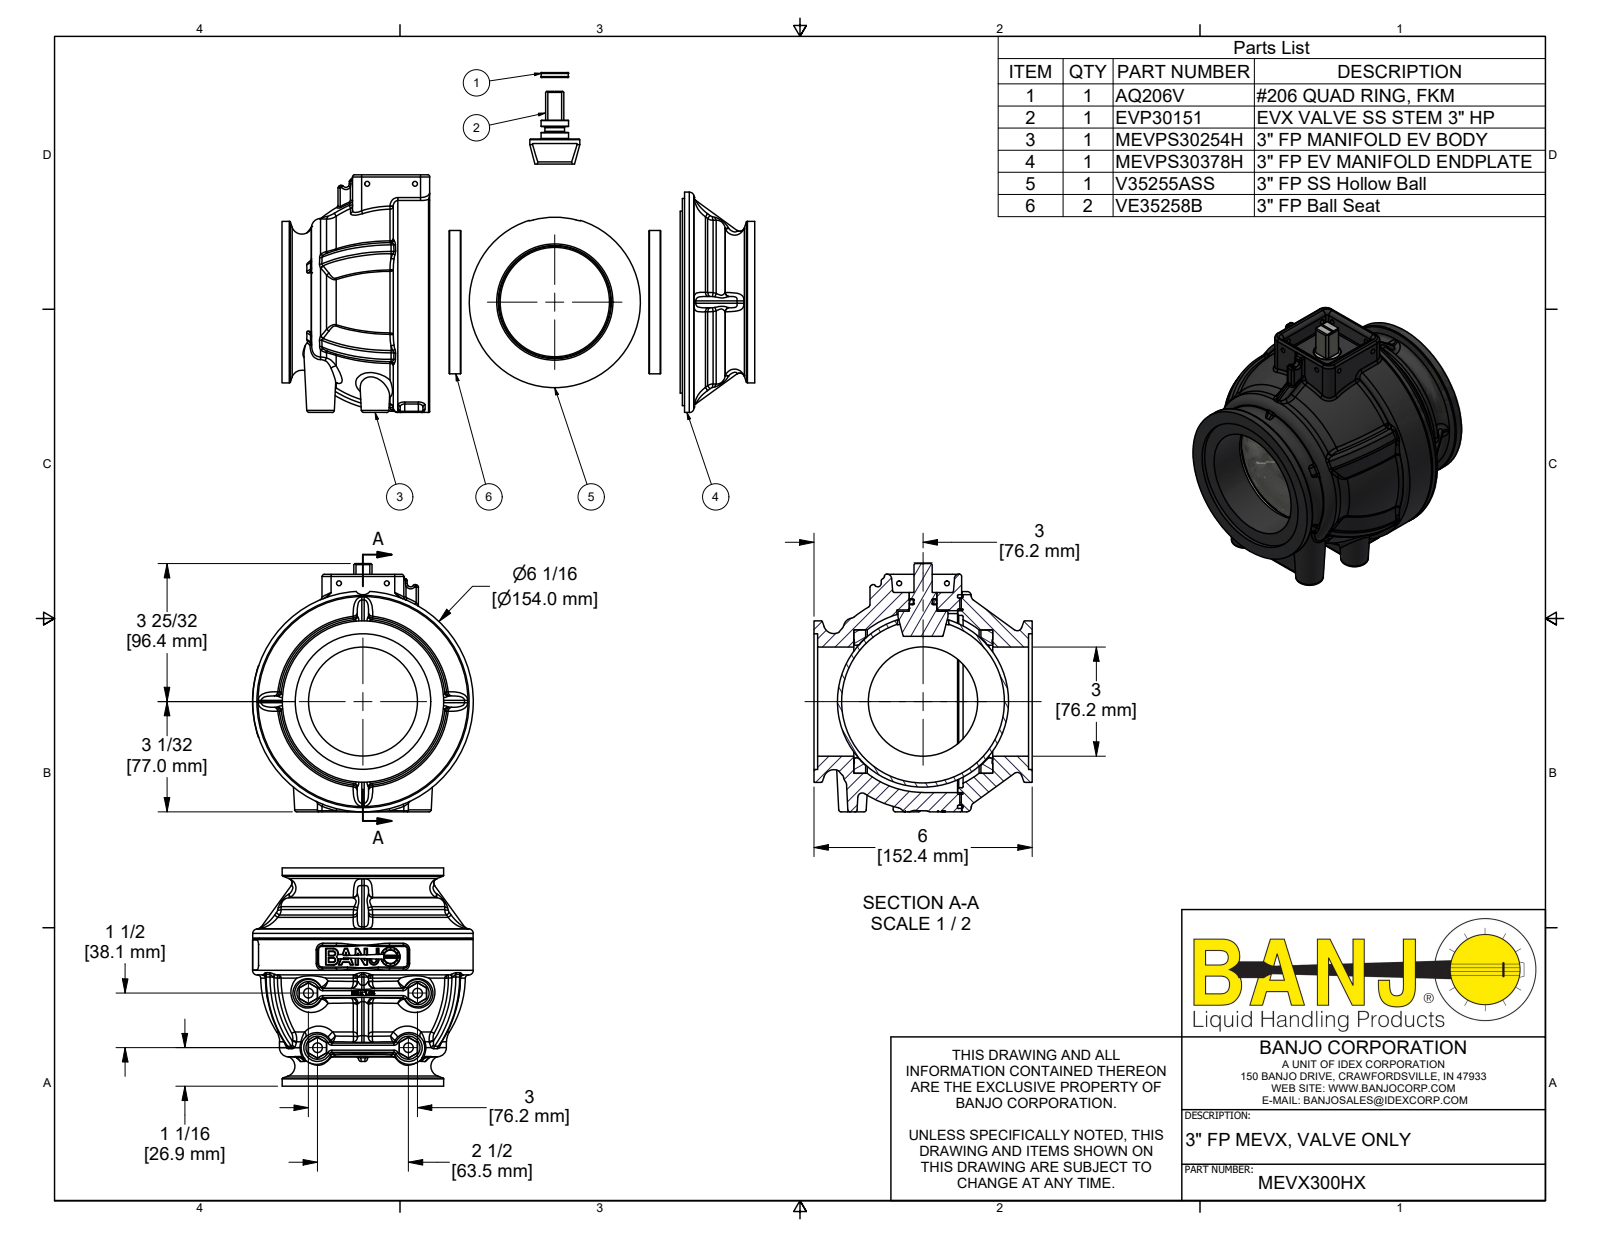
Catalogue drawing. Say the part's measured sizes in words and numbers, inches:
The part is named "MEVX300HX; AQ206V; EVP30151; MEVPS30254H (+6 more)". Its 3-D file was written by "Autodesk Inventor 2022 (AUTOMOTIVE_DESIGN)". It is 12 solids with 1307 faces: 498 planar, 213 cylindrical and 596 other. Overall it measures 6.825 by 6.063 by 6 inches. Its volume is 54.44 cubic inches and its surface area 431.2 square inches. Round holes: 4 of diameter 0.135, 4 of diameter 0.262, 4 of diameter 0.433, 2 of diameter 3, 1 of diameter 0.54, 1 of diameter 0.76, 1 of diameter 1.437, 1 of diameter 3.095, 1 of diameter 3.129, 1 of diameter 3.73, 1 of diameter 3.944, 1 of diameter 4.735. Round bosses or shafts: 1 of diameter 6.063, 1 of diameter 5.695, 1 of diameter 4.529, 1 of diameter 4.44, 1 of diameter 3.94, 1 of diameter 1.375, 1 of diameter 0.755, 1 of diameter 0.538. Partial cylindrical surfaces (rounded edges, fillets, slot ends): 39 of radius 0.06, 30 of radius 0.125, 8 of radius 0.03, 5 of radius 0.25, 4 of radius 0.118, 3 of radius 0.06, 3 of radius 0.09, 3 of radius 3. The main face-to-face distances are 0.1, 3.82, 5.9, 0.04, 2.955, 1.95, 0.905, 2.915, 0.865, 3.95. The hole center spacings are 3.316, 1.521, 1.563, 2.308, 3.133, 0.941, 1.246, 1.312.
